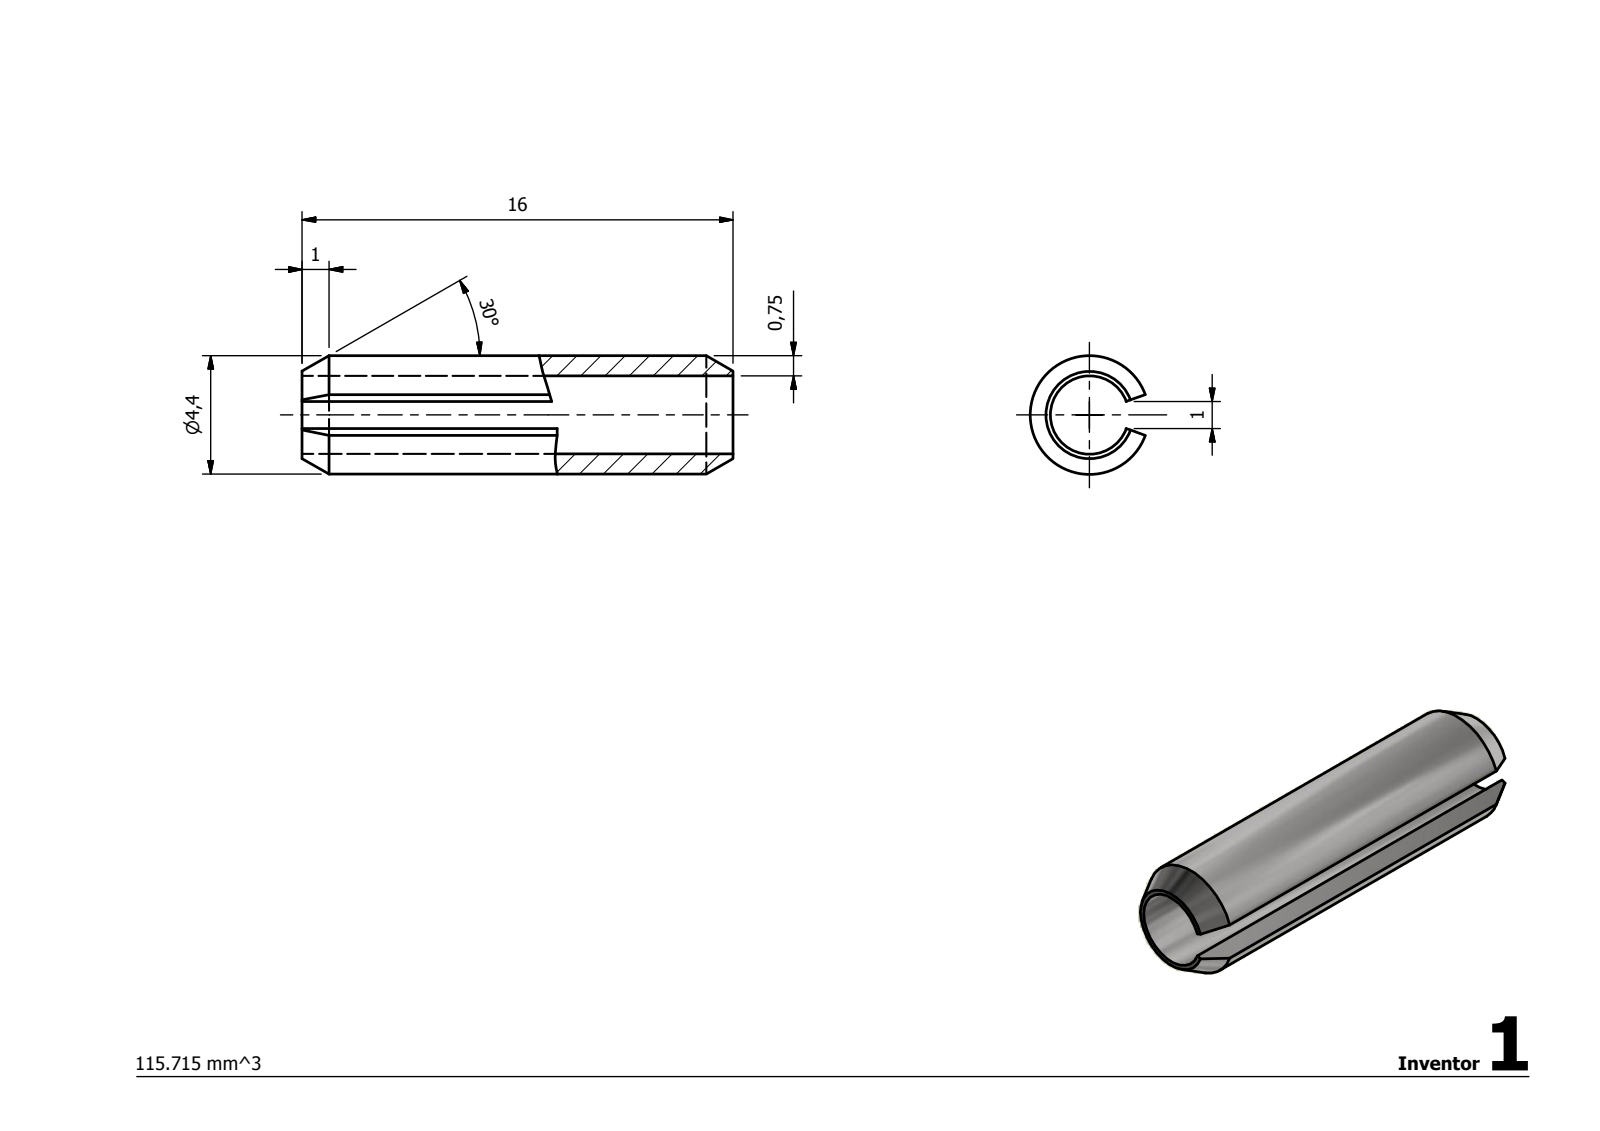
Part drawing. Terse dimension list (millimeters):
written by: Autodesk Inventor 2014 (AUTOMOTIVE_DESIGN)
unit: mm
bodies: 1 solid, 8 faces (4 planar, 2 cylindrical, 2 other)
size: 16 × 4.4 × 4.26
volume: 116 mm³; area: 352 mm²
holes: 1× ⌀2.9
bosses: 1× ⌀4.4
face distances: 16
